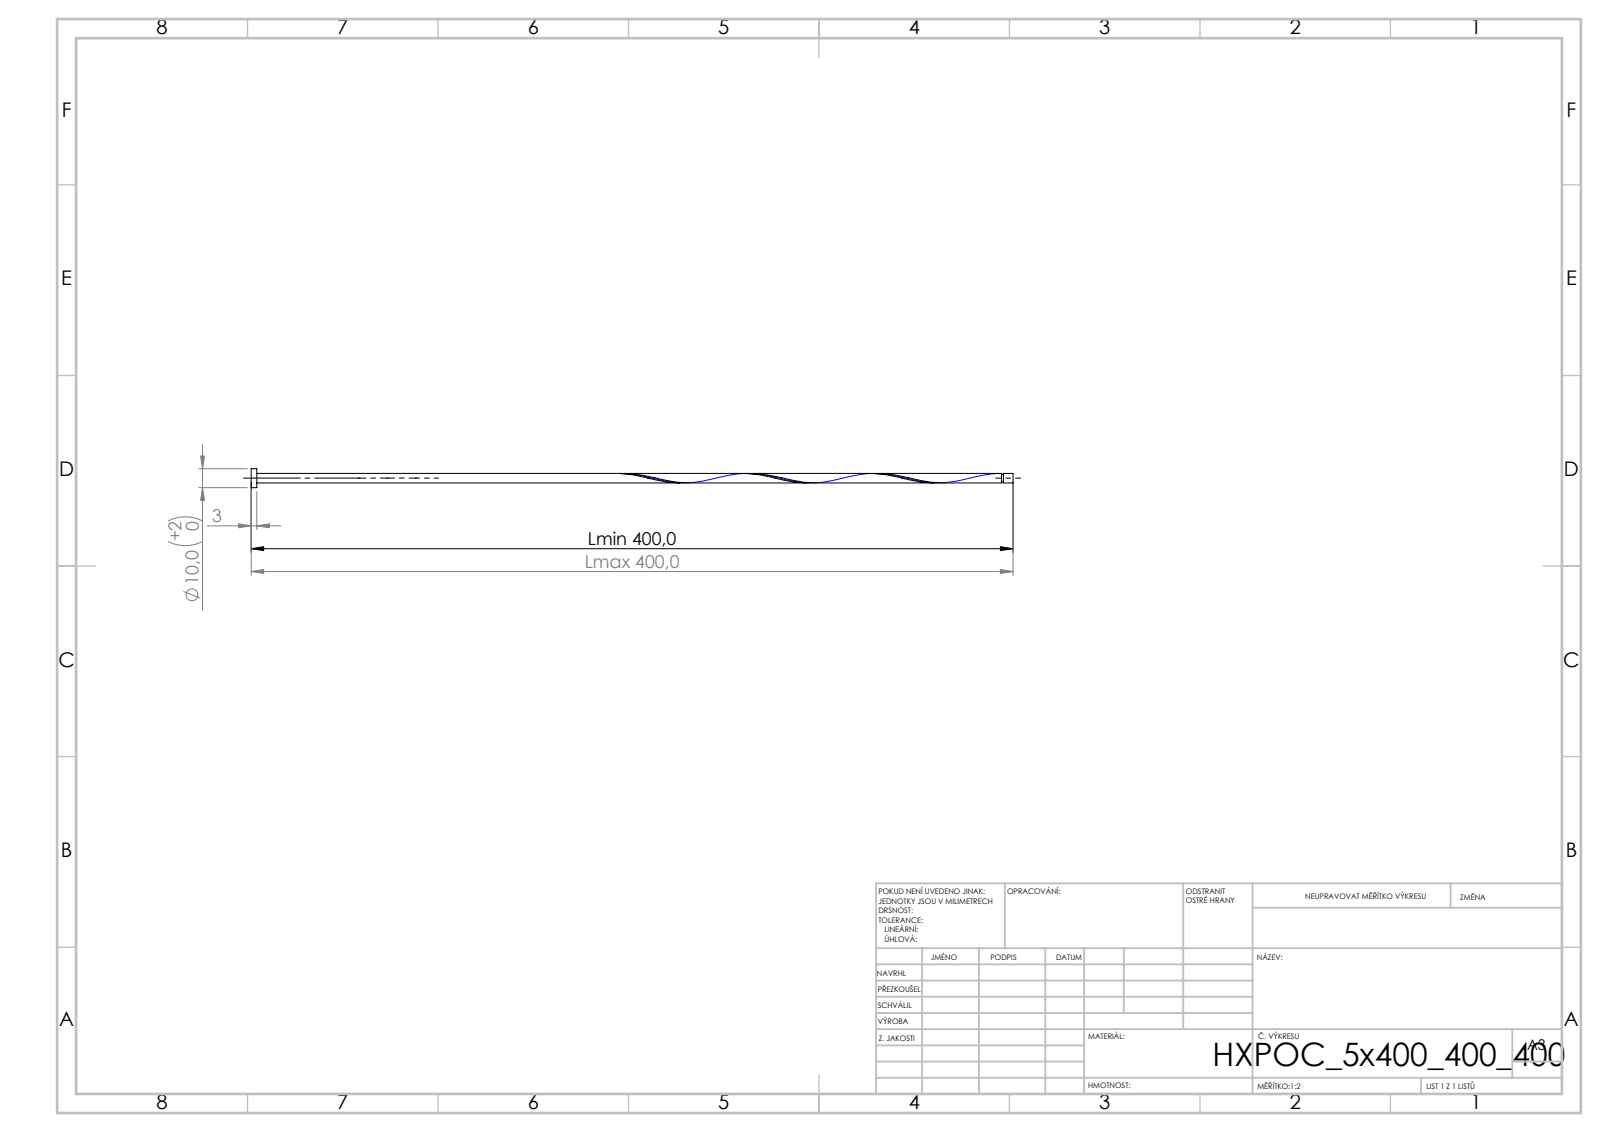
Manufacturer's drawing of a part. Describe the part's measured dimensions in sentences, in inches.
Its 3-D file was written by "SolidWorks 2019 (CONFIG_CONTROL_DESIGN)". It is 1 solid with 16 faces: 6 planar, 9 cylindrical and 1 other. Overall it measures 15.748 by 0.394 by 0.394 inches. Its volume is 0.592 cubic inches and its surface area 13.47 square inches. Round bosses or shafts: 1 of diameter 0.394, 1 of diameter 0.197, 1 of diameter 0.157. The main face-to-face distances are 0.118, 15.748, 15.63, 15.547, 15.429, 0.201, 15.508, 15.39, 0.039, 0.24.
